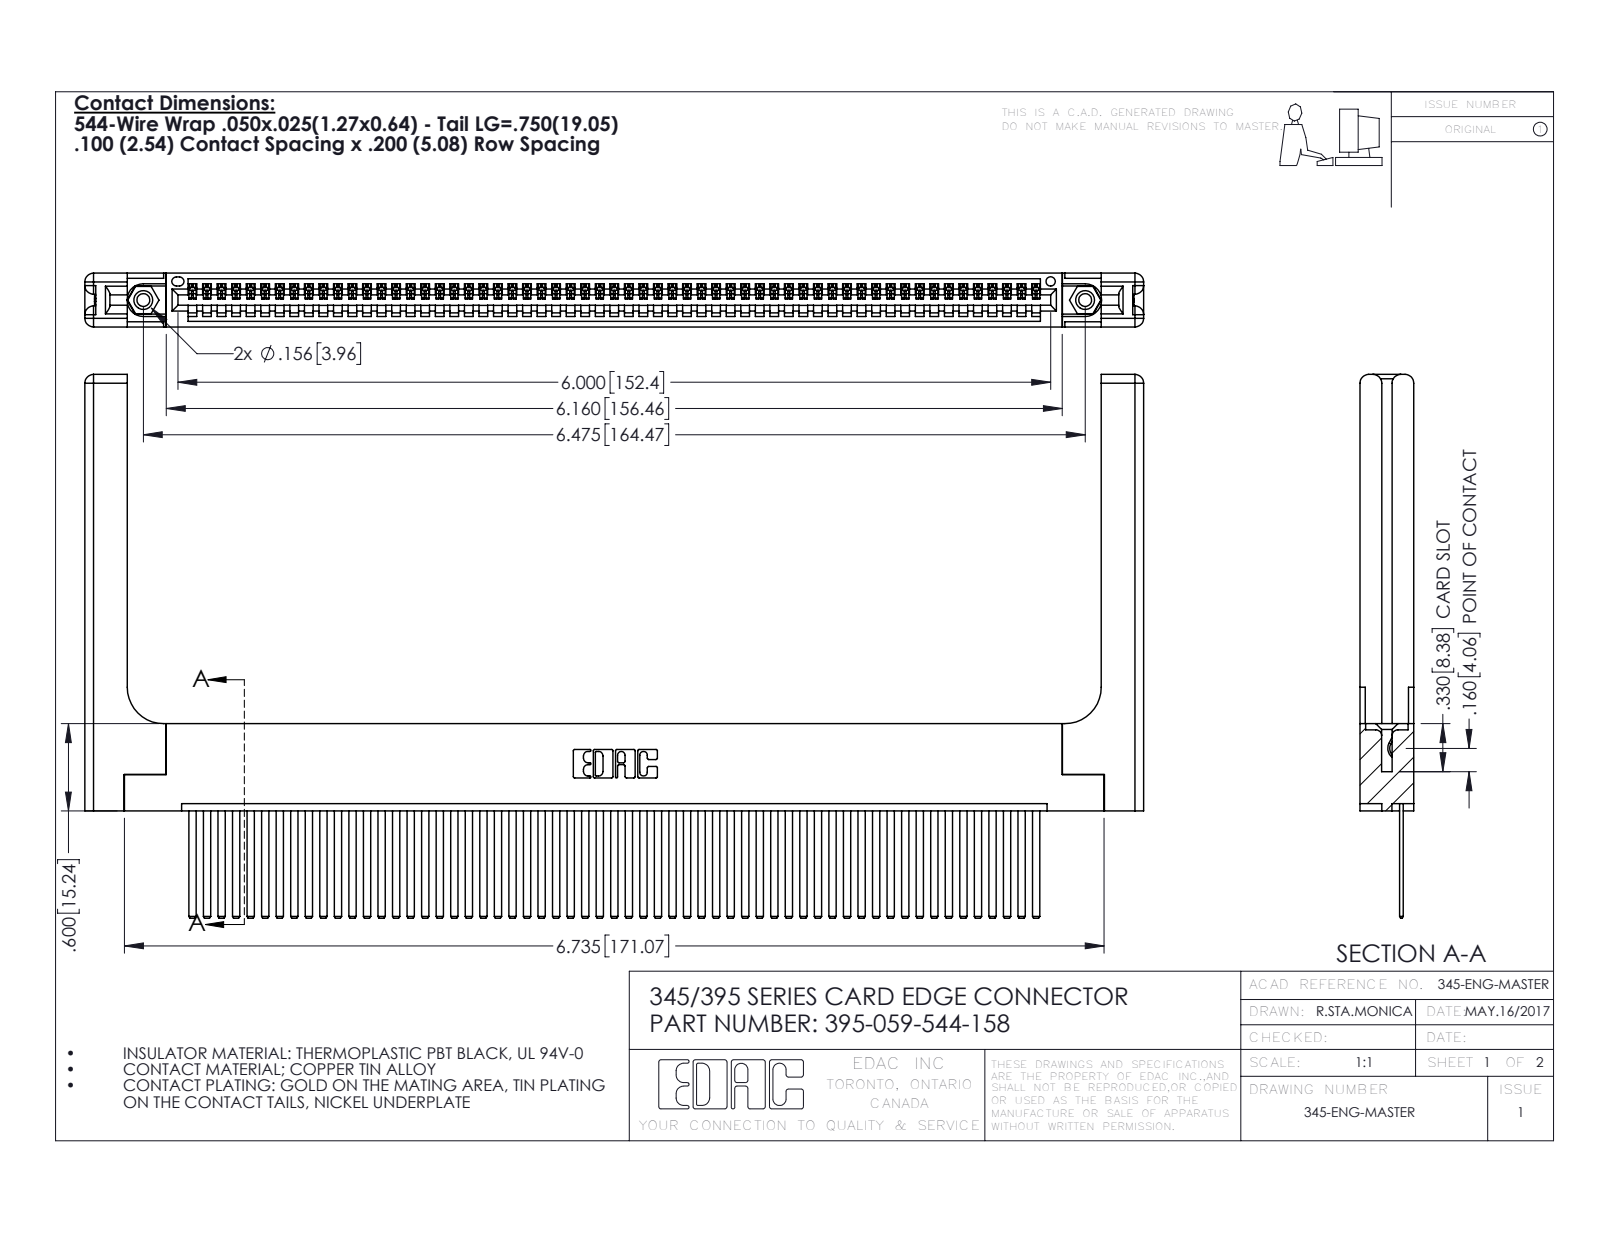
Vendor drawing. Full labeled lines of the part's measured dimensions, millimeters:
Part name (STEP PRODUCT): 395-059-544-158; 345-250-001_345-250-001-102; 345-220-058_345-220-058; 345-292-001_345-293-144 (+1 more)
STEP written by: SolidWorks 2016 (CONFIG_CONTROL_DESIGN)
Units: millimetres
Bodies: 64 solids, 3450 faces (2352 planar, 1038 cylindrical, 60 other)
Overall size (bounding box): 184.9 × 94.9 × 9.4
Volume: 26 890 mm³ · Surface area: 32 020 mm²
Round holes (diameter × count): ⌀2.3 ×2, ⌀3.2 ×2, ⌀4 ×2, ⌀1.6 ×1
Round bosses / shafts (diameter × count): ⌀3.9 ×2
Partial cylindrical surfaces — rounded edges, fillets, slot ends (radius × count): R0.2 ×118, R0.3 ×22, R1.5 ×16, R0.2 ×6, R0.8 ×6, R0.7 ×3, R0.8 ×2, R0.8 ×2
Main face-to-face distances: 1.8, 7.6, 9.4, 2.5, 6.9, 0.6, 5.1, 5.7, 3.8, 3.8
Hole centre spacings: 6.9, 158.5, 164.5
